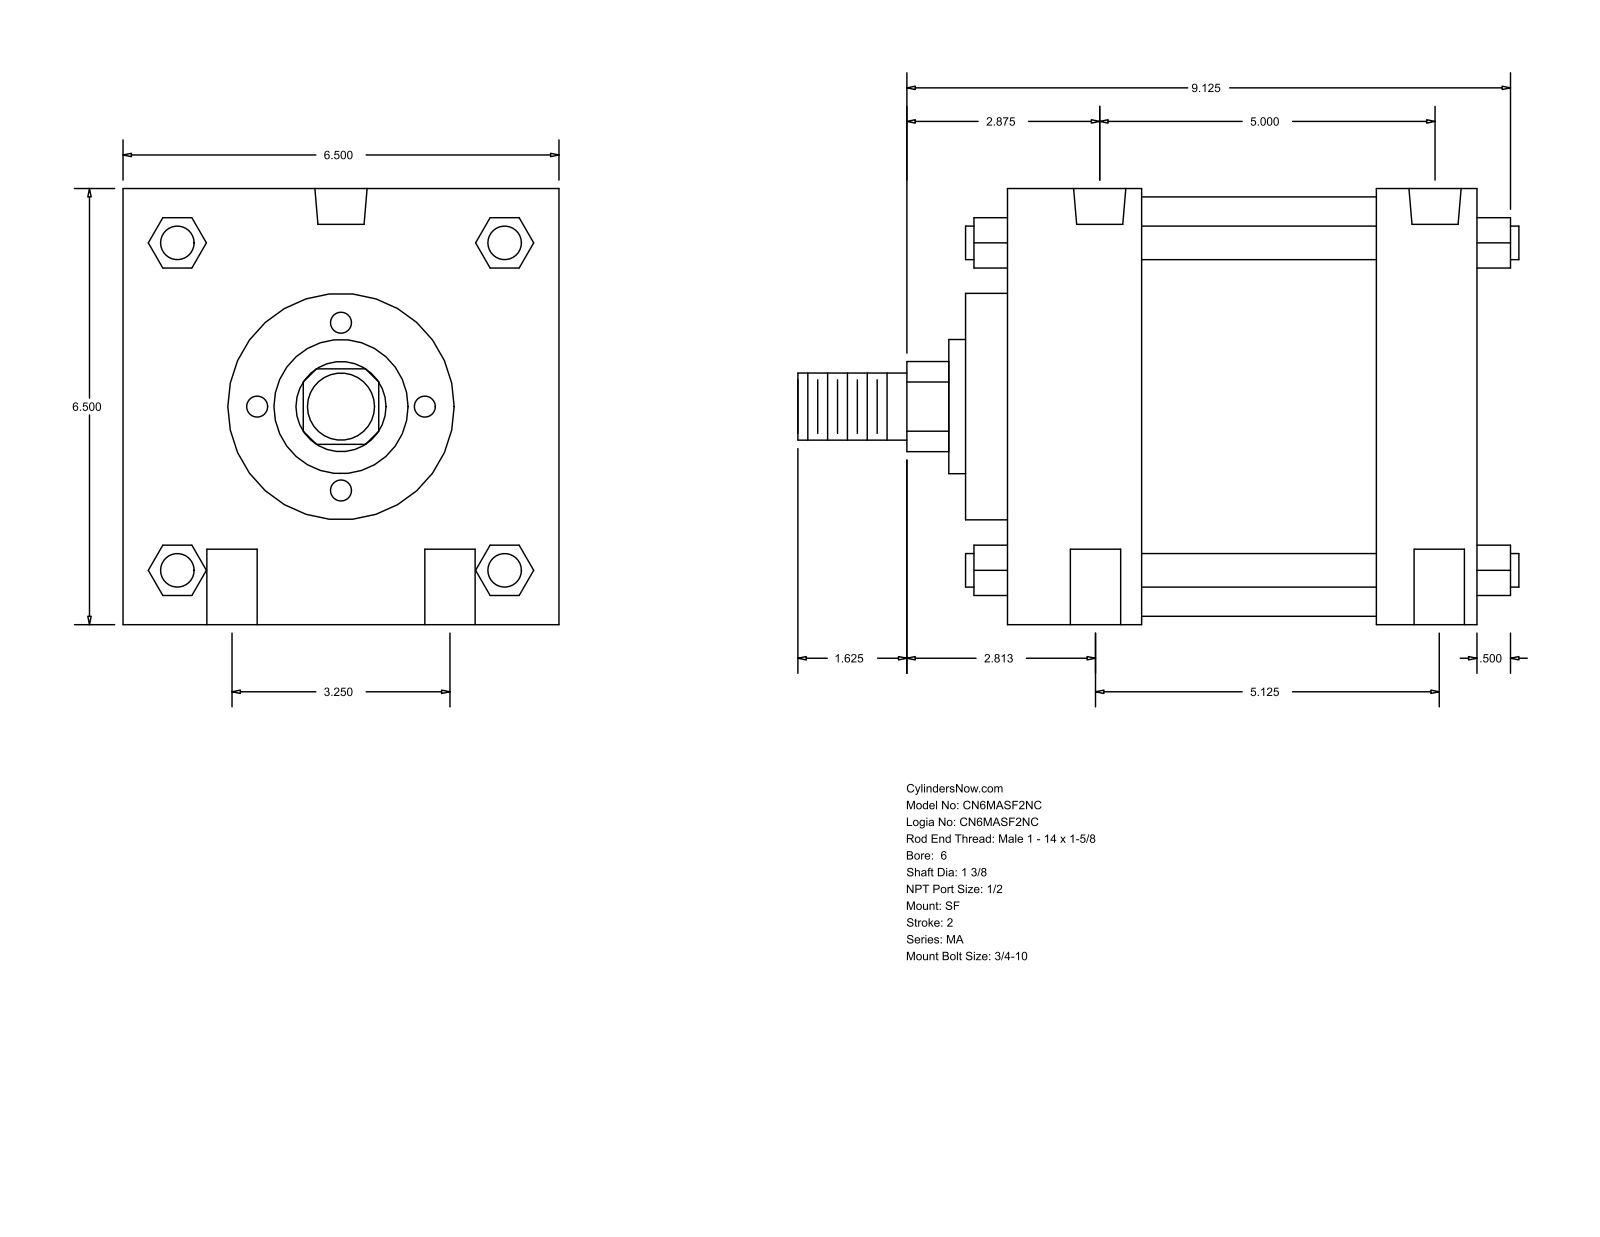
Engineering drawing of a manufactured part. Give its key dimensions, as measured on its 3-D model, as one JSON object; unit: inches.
{"part_name": "MA_SF__0600_1.375", "step_written_by": "GSSL Pune (CONFIG_CONTROL_DESIGN)", "units": "inches", "bodies": {"solids": 0, "faces": 126, "planar": 95, "cylindrical": 31, "other": 0}, "overall_size": [10.75, 6.5, 6.5], "round_holes": [[0.75, 4], [0.687, 2], [0.778, 2]], "round_bosses_or_shafts": [[0.5, 4], [6.25, 1], [3.375, 1], [2, 1], [1.375, 1], [1, 1]], "partial_cylinders_radius": [[0.672, 1]], "face_to_face_distances": [6.5, 7, 5.5, 2, 1.5, 3.5, 5, 2.625, 0.625, 6.125], "hole_center_spacings": [1.626, 3.25, 5, 5.125, 5.317, 5.317, 6.068]}
